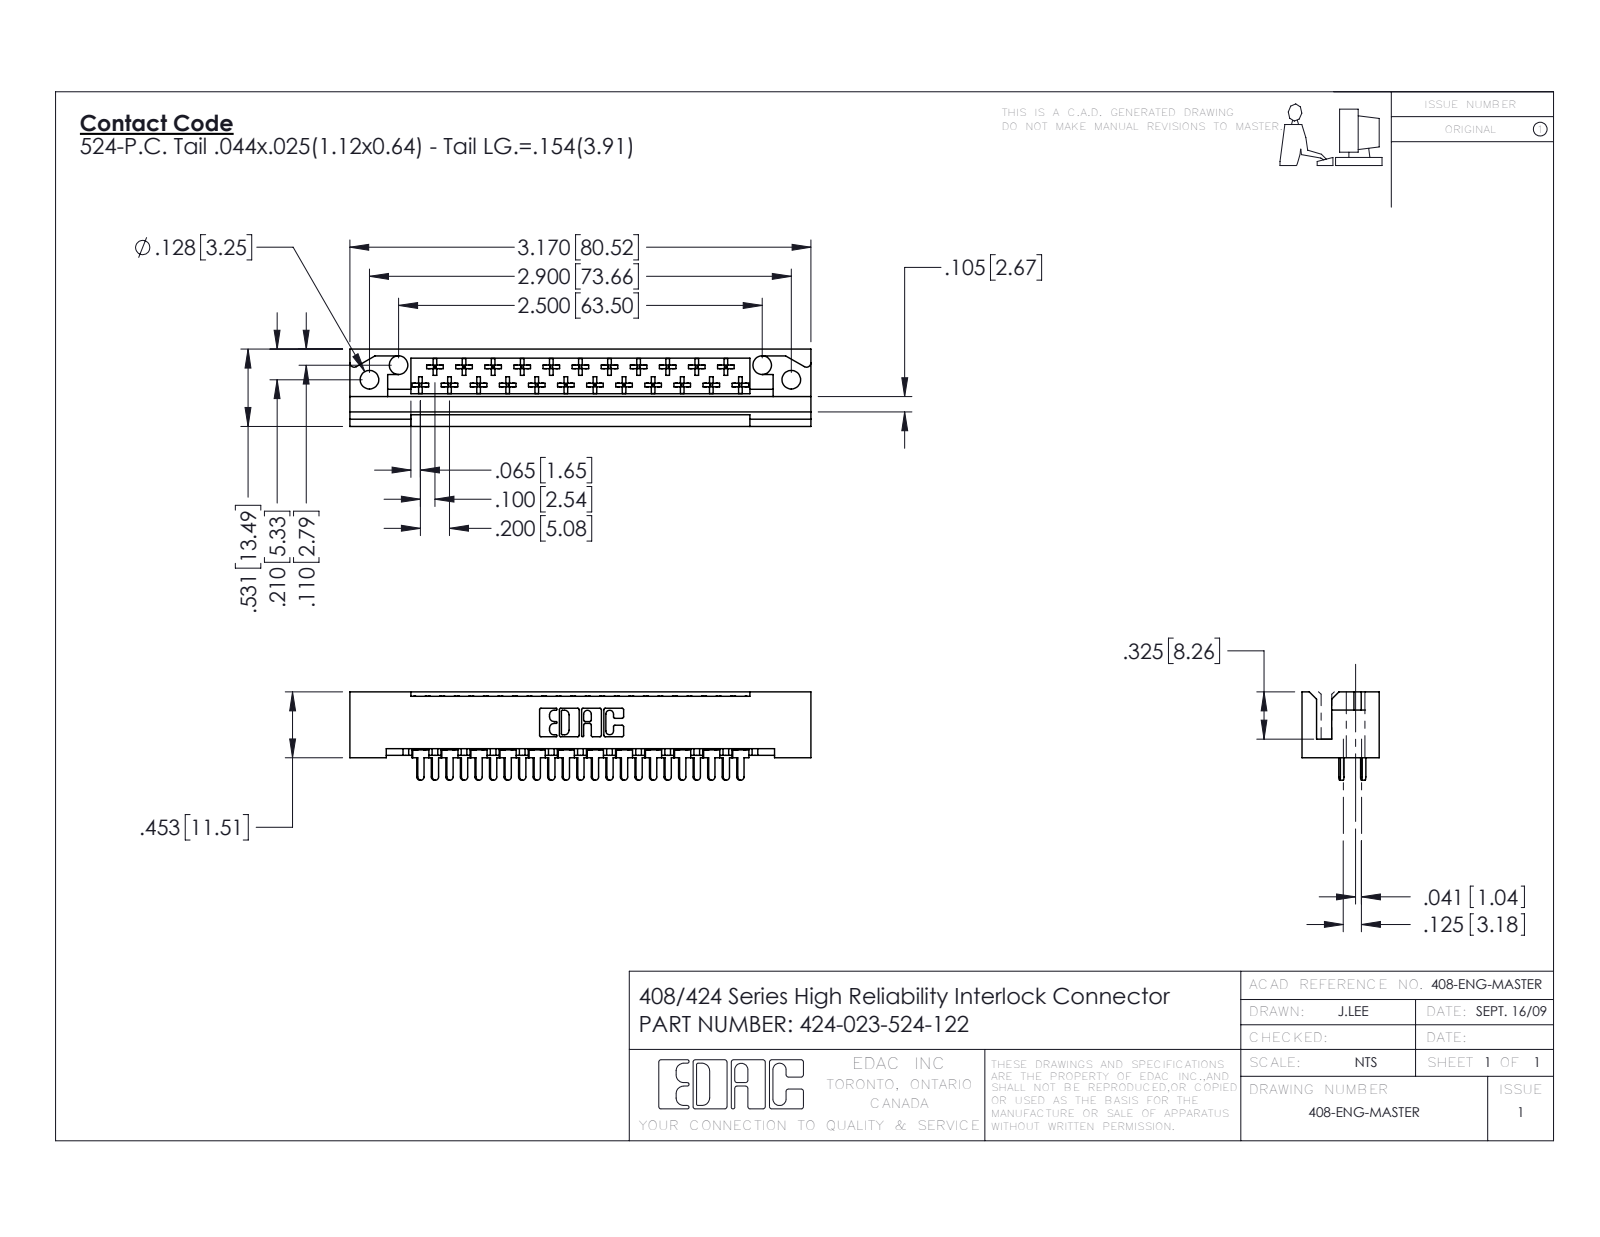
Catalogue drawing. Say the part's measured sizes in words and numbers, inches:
The part is named "424 Part_023; 424-023-524-122; 408-290-001_408-290-124 - Bottom; 408-290-001_408-290-124 - Top". Its 3-D file was written by "SolidWorks 2016 (CONFIG_CONTROL_DESIGN)". It is 24 solids with 1410 faces: 1055 planar, 263 cylindrical and 92 other. Overall it measures 3.17 by 0.607 by 0.531 inches. Its volume is 0.505 cubic inches and its surface area 16.41 square inches. Round holes: 4 of diameter 0.128. Partial cylindrical surfaces (rounded edges, fillets, slot ends): 138 of radius 0.01, 25 of radius 0.02, 23 of radius 0.022, 22 of radius 0.01, 6 of radius 0.007, 6 of radius 0.031, 3 of radius 0.026, 2 of radius 0.03. The main face-to-face distances are 0.1, 0.296, 0.025, 0.531, 0.125, 0.431, 0.025, 0.105, 0.326, 0.205. The hole center spacings are 0.224, 2.702, 2.5, 2.9.
